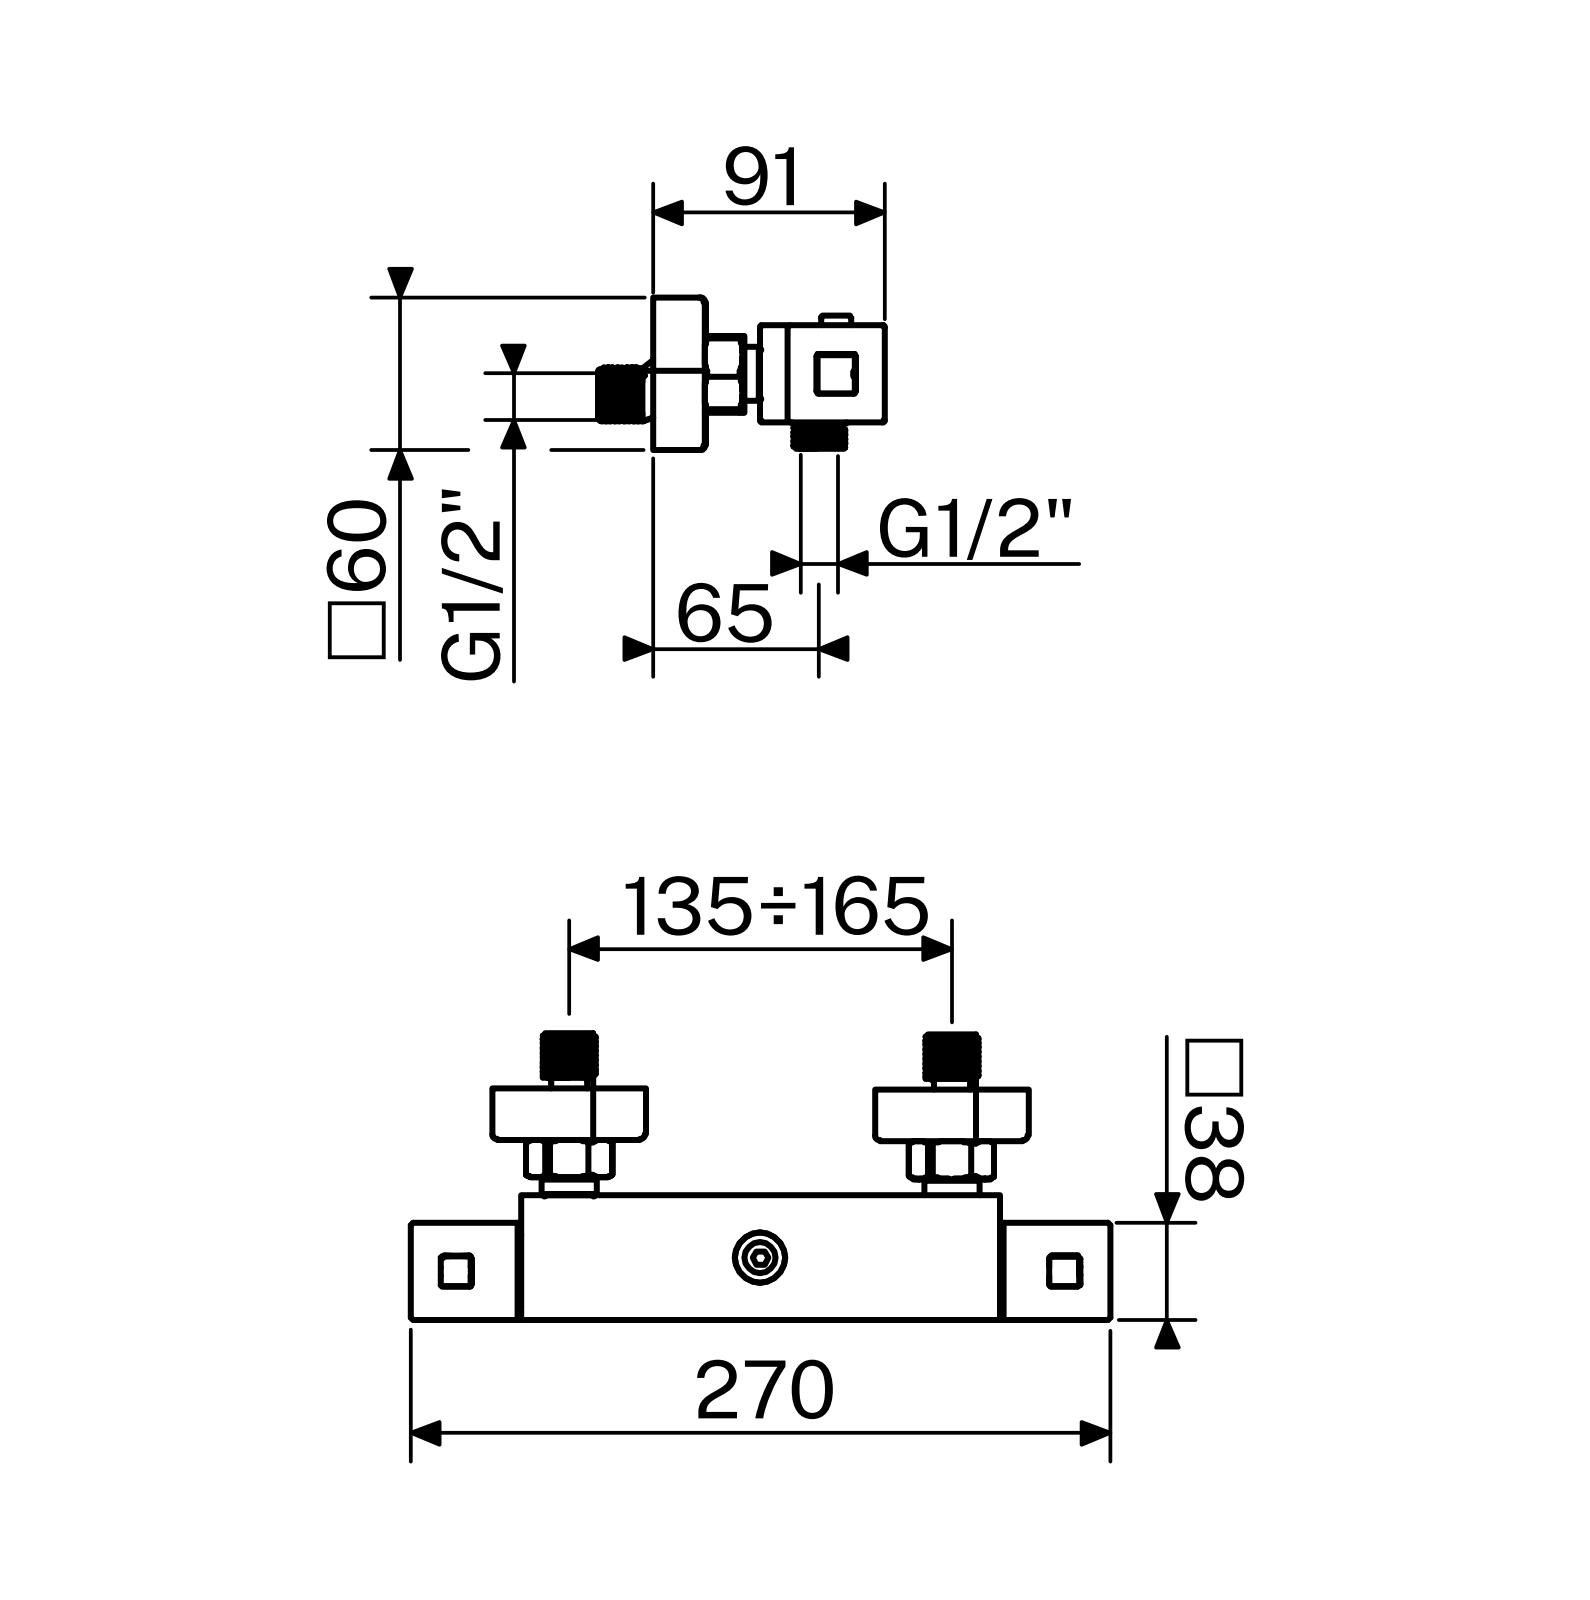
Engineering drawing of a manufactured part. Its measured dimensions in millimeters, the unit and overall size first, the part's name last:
Units: millimetres
Overall size (bounding box): 1500.3 × 551.25 × 269
Round holes (diameter × count): ⌀1.5 ×80, ⌀1.7 ×80, ⌀3.1 ×80, ⌀1 ×40, ⌀16.5 ×3, ⌀18.2 ×3, ⌀18.5 ×3, ⌀22.2 ×3, ⌀24 ×3, ⌀24.5 ×3, ⌀4.8 ×2, ⌀6 ×2
Round bosses / shafts (diameter × count): ⌀5 ×84, ⌀10 ×82, ⌀3.3 ×80, ⌀2.5 ×40, ⌀20 ×5, ⌀15 ×4, ⌀28 ×2, ⌀26.4 ×2
Partial cylindrical surfaces — rounded edges, fillets, slot ends (radius × count): R0.5 ×136, R1.5 ×132, R1 ×109, R0.3 ×46, R0.2 ×26, R2 ×14, R5 ×10, R4 ×8
Main face-to-face distances: 1, 4, 3, 5, 2.5, 38, 46.5, 35.5, 1293.7, 1289.7
Hole centre spacings: 58.7, 26.25, 37.12, 52.5, 4.5, 83.01, 9, 5.81
Volume: 726 663 mm³ · Surface area: 776 912 mm²
Bodies: 116 solids, 6711 faces (1363 planar, 2262 cylindrical, 3086 other)
Part name (STEP PRODUCT): F051002-001_6; 82040002_8_1_2_1; 82040002_8_1_2_2; 82040002_8_1_2 (+8 more)
STEP written by: CREO PARAMETRIC BY PTC INC, 2020281 (CONFIG_CONTROL_DESIGN)
